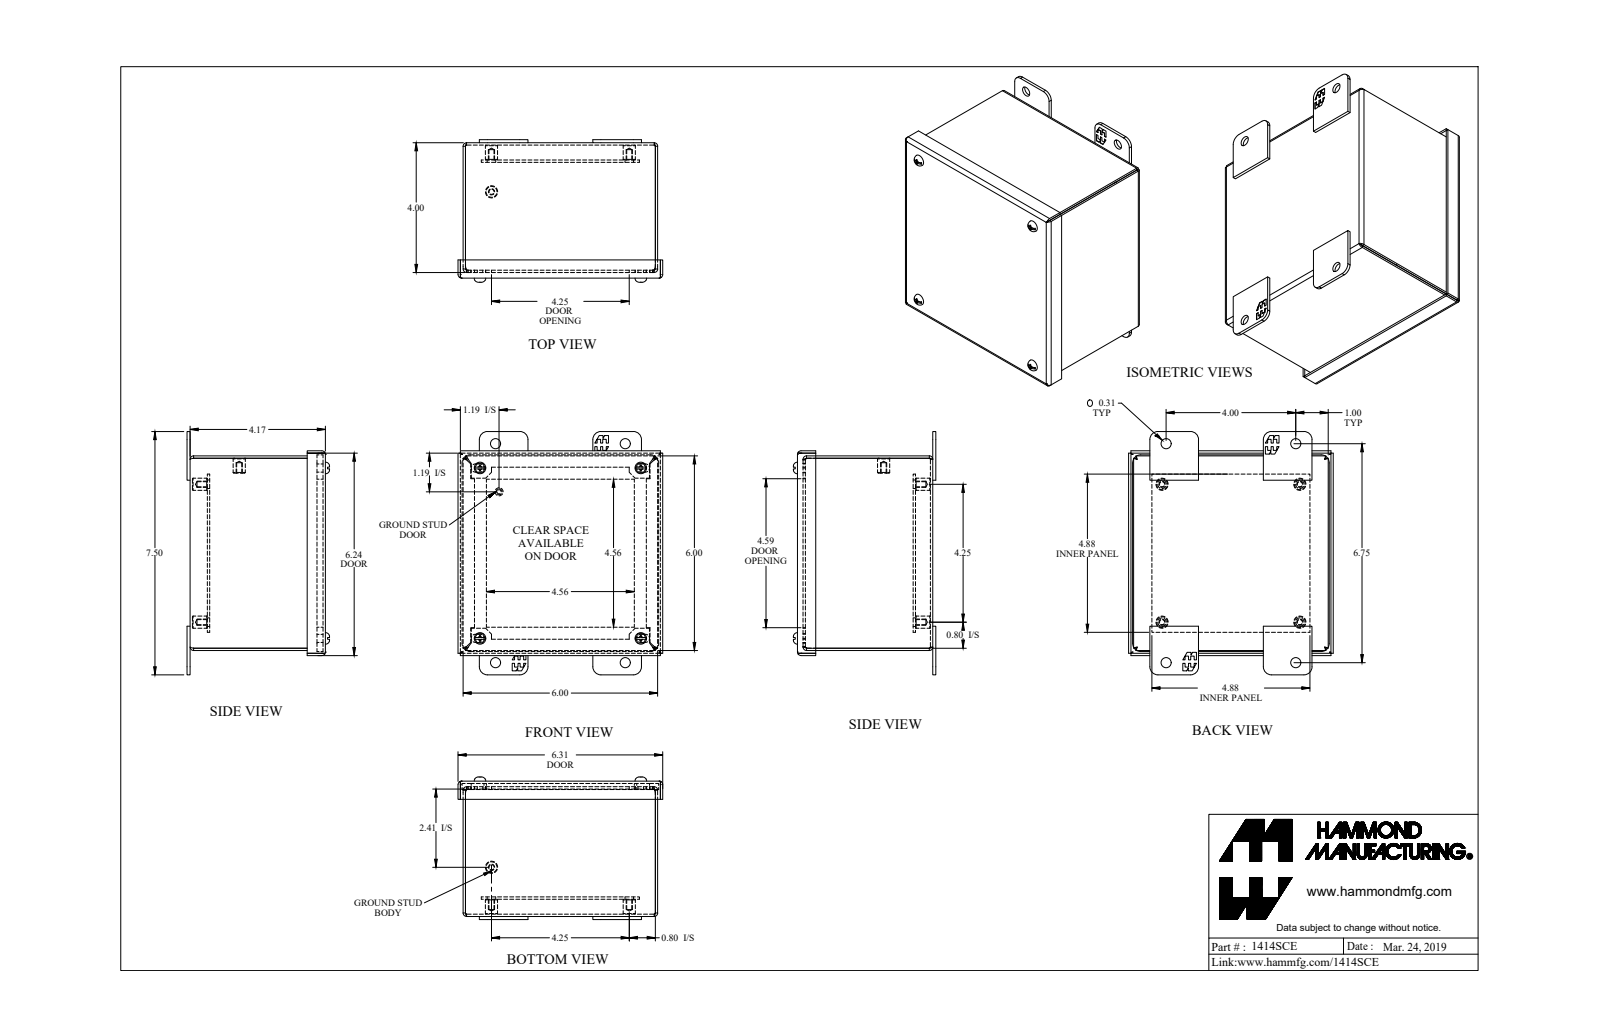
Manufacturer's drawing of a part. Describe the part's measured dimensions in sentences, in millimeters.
The part is named "1414SCE". Its 3-D file was written by "SolidWorks 2018 (AUTOMOTIVE_DESIGN)". It is 26 solids with 642 faces: 442 planar, 140 cylindrical and 60 other. Overall it measures 190.5 by 160.3 by 111.6 millimeters. Its volume is 314 000 cubic millimeters and its surface area 321 100 square millimeters. Round holes: 5 of diameter 4, 4 of diameter 4, 4 of diameter 6.4, 4 of diameter 6.7, 4 of diameter 7.9. Round bosses or shafts: 5 of diameter 9.5, 4 of diameter 9.9, 4 of diameter 7, 4 of diameter 4.8, 4 of diameter 3.8, 1 of diameter 6.4, 1 of diameter 4.8. Partial cylindrical surfaces (rounded edges, fillets, slot ends): 12 of radius 6.4, 8 of radius 0.9, 8 of radius 2.7, 8 of radius 3.2, 8 of radius 7.1, 4 of radius 0.2, 4 of radius 1.2, 4 of radius 2. The main face-to-face distances are 1.8, 150.6, 104.1, 90.6, 13.5, 148.7, 152.4, 106, 102.3, 92.5. The hole center spacings are 109.5, 108, 108, 117.7, 15.6, 121, 139.8, 31.9.
